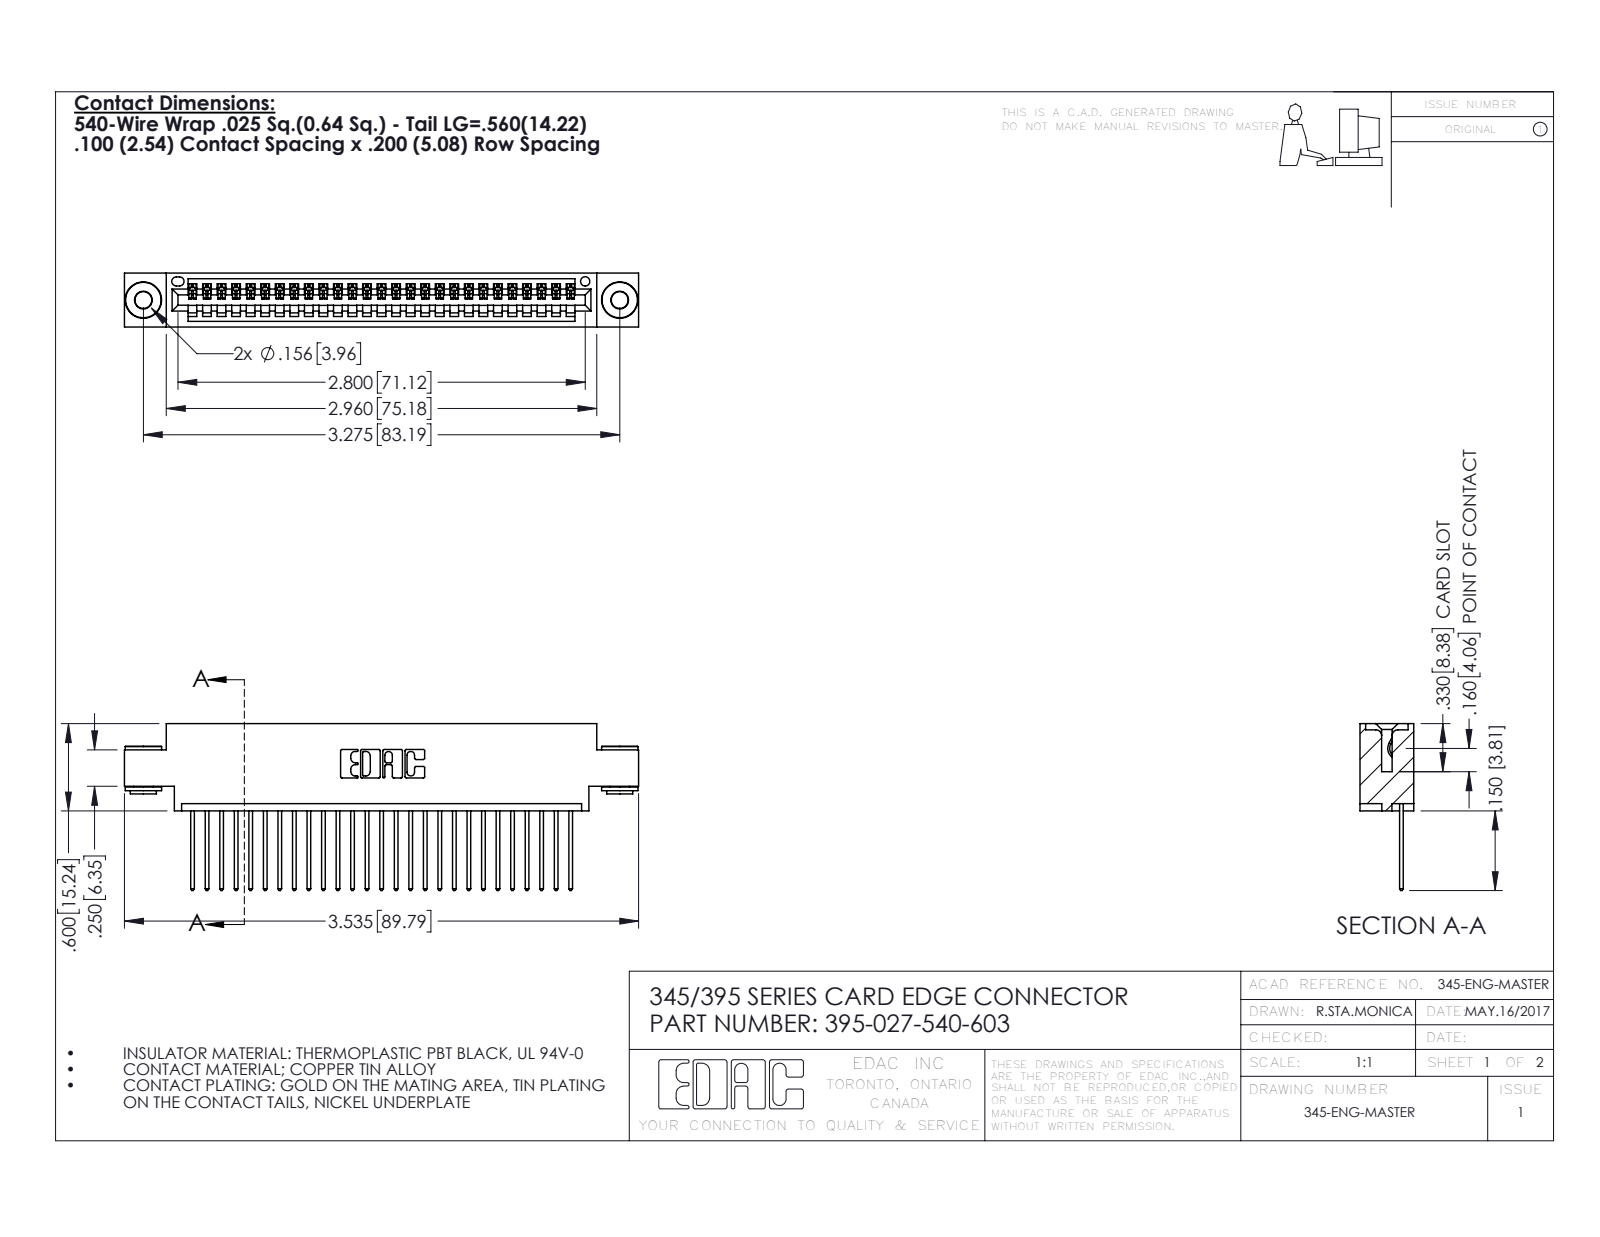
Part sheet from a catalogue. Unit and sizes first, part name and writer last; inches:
Units: inches
Overall size (bounding box): 3.535 × 1.147 × 0.37
Round holes (diameter × count): ⌀0.116 ×2, ⌀0.156 ×2, ⌀0.064 ×1
Round bosses / shafts (diameter × count): ⌀0.25 ×2, ⌀0.18 ×2, ⌀0.136 ×2
Partial cylindrical surfaces — rounded edges, fillets, slot ends (radius × count): R0.006 ×54, R0.01 ×54, R0.01 ×22, R0.007 ×6, R0.031 ×6, R0.026 ×3, R0.031 ×2, R0.04 ×2
Main face-to-face distances: 0.072, 0.298, 0.37, 0.098, 0.272, 0.025, 0.2, 0.225, 0.175, 0.1
Hole centre spacings: 0.27, 3.04, 3.275
Volume: 0.509 in³ · Surface area: 17.82 in²
Bodies: 30 solids, 1734 faces (1174 planar, 552 cylindrical, 8 other)
Part name (STEP PRODUCT): 395-027-540-603; 345 Part_0.170 Offset - 0.156 Dia-TH; 345-250-002_345-250-002-102; 345-292-001_345-293-140
STEP written by: SolidWorks 2016 (CONFIG_CONTROL_DESIGN)
